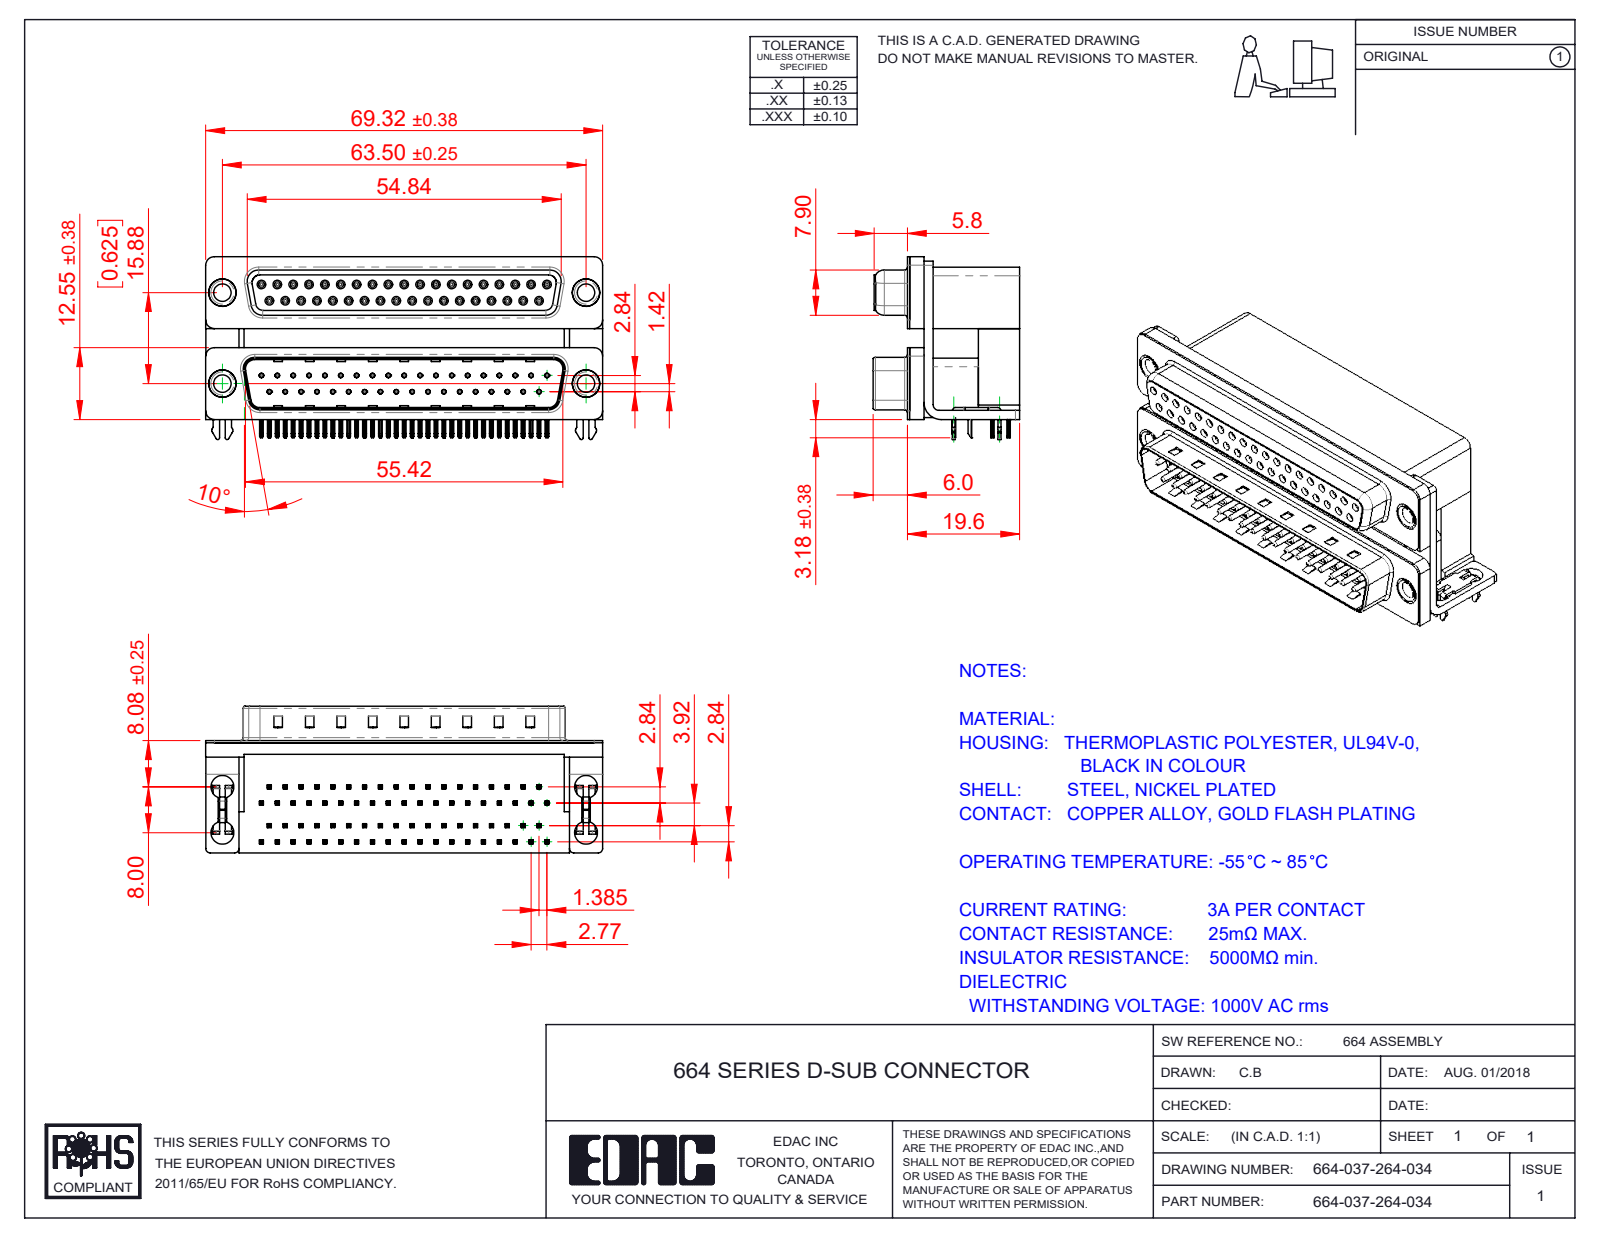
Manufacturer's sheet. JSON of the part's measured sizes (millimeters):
{"part_name": "664 Mounting Bracket_2ProngL; 664 Contact Bottom Upper_L; 664 Shell Receptacle_37 Contacts; 664 2 Prong Board Lock_3 (+8 more)", "step_written_by": "SolidWorks 2020 (CONFIG_CONTROL_DESIGN)", "units": "millimeters", "bodies": {"solids": 87, "faces": 9013, "planar": 4843, "cylindrical": 2191, "other": 1979}, "overall_size": [69.32, 31.93, 25.6], "volume_mm3": 29774, "surface_area_mm2": 31647, "round_holes": [[0.8, 74], [0.35, 37], [0.9, 37], [4, 8], [3.05, 4], [3.5, 4], [4.8, 4], [5, 4]], "round_bosses_or_shafts": [[1.2, 37], [0.75, 37], [4.9, 4], [4.75, 4], [3.85, 4]], "partial_cylinders_radius": [[0.1, 298], [0.25, 158], [0.15, 148], [0.12, 74], [0.35, 74], [0.34, 37], [0.28, 18], [0.5, 16]], "face_to_face_distances": [0.4, 19.2, 7.2, 12, 2.19, 15.52, 2.84, 26.22, 10.7, 13.33], "hole_center_spacings": [2.77, 5.54, 3.16, 8.31, 11.08, 13.85, 16.62, 19.39]}
